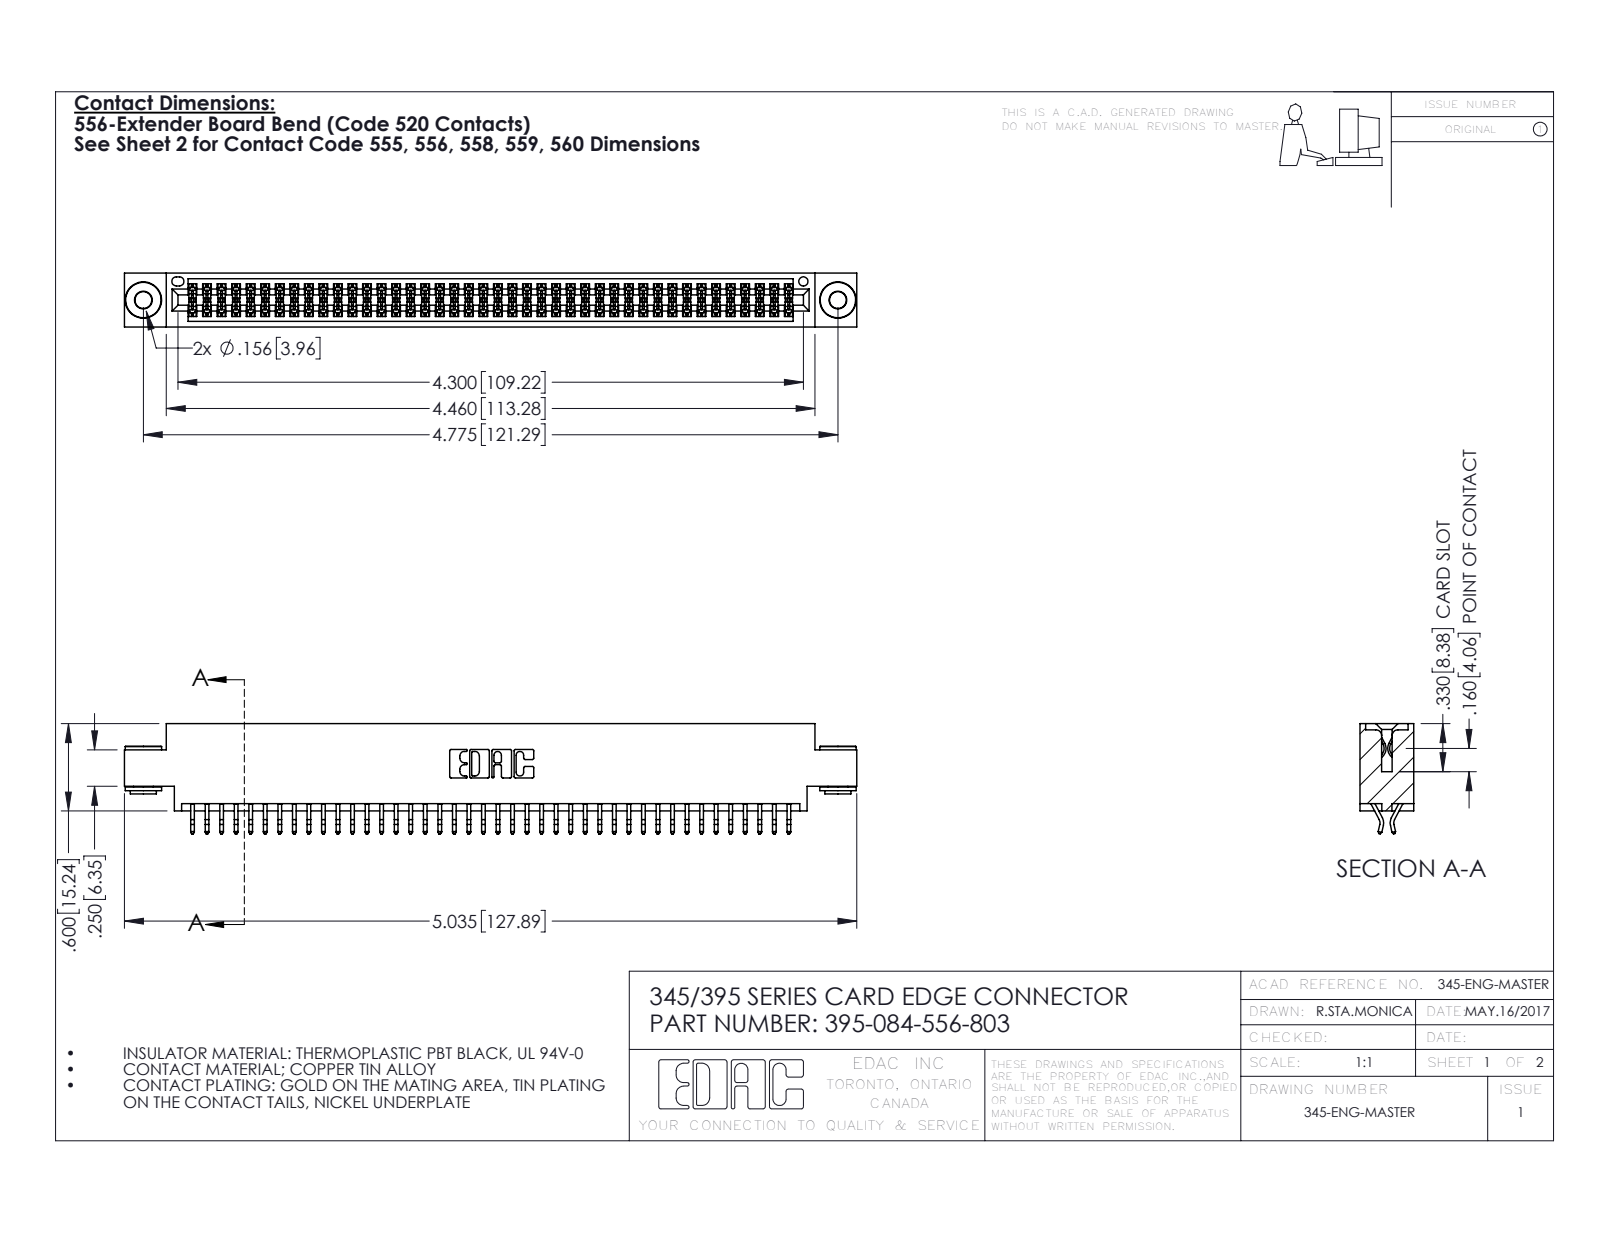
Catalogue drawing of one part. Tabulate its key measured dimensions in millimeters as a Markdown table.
| quantity | value |
| --- | --- |
| part name | 345-250-002_345-250-002-102; 345-292-001_556 Tail; 345 Part_0.170 Offset - 0.156 Dia-TH; 395-084-556-803 |
| STEP written by | SolidWorks 2016 (CONFIG_CONTROL_DESIGN) |
| units | millimeters |
| bodies | 87 solids, 4872 faces (3202 planar, 1662 cylindrical, 8 other) |
| overall size | 127.9 × 19.2 × 9.4 |
| volume | 12 300 mm³ |
| surface area | 18 500 mm² |
| round holes (diameter × count) | 2.9 × 2, 4 × 2, 1.6 × 1 |
| round bosses / shafts (diameter × count) | 6.4 × 2, 4.6 × 2, 3.5 × 2 |
| partial cylindrical surfaces (radius × count) | 0.2 × 126, 0.3 × 22, 0.2 × 6, 0.8 × 6, 0.7 × 3, 0.3 × 2, 0.4 × 2, 0.5 × 2 |
| main face-to-face distances | 1.8, 7.6, 9.4, 5.1, 0.6, 2.5, 6.9, 5.7, 4.4, 3.8 |
| hole center spacings | 6.9, 115.3, 121.3 |
